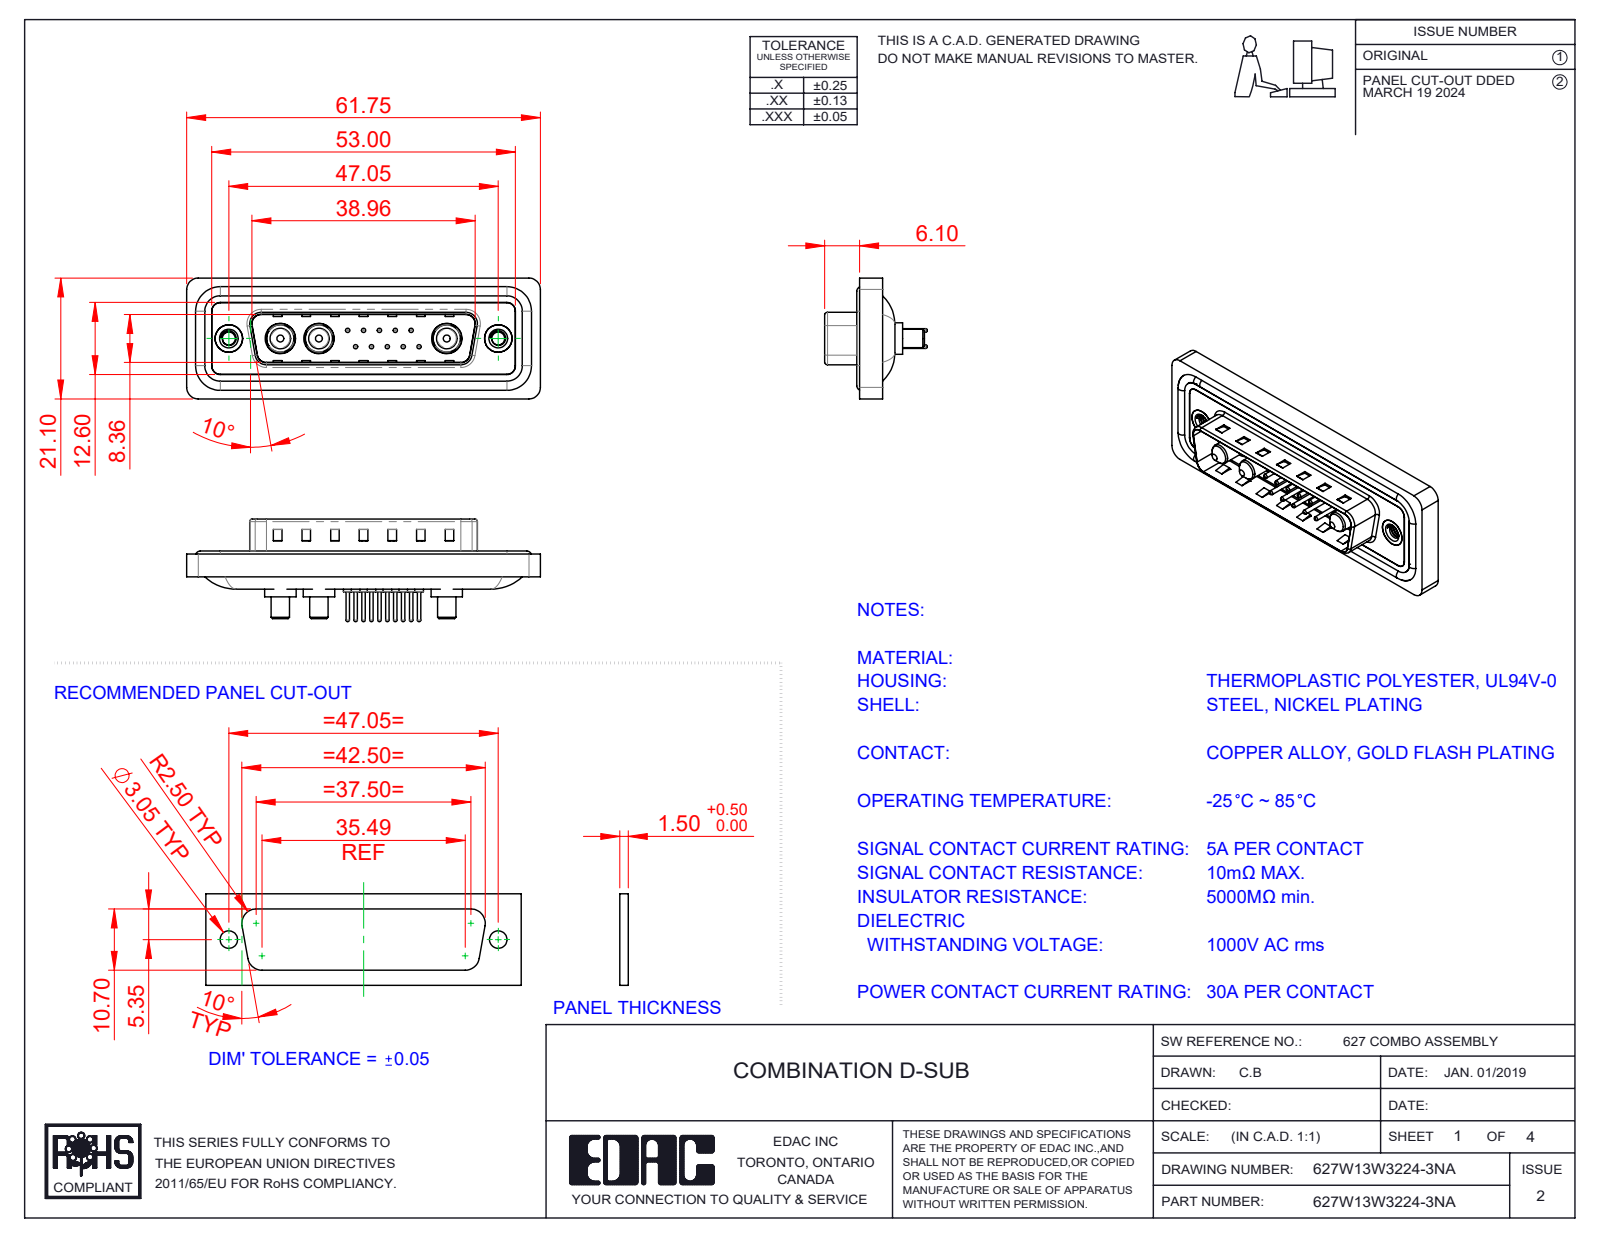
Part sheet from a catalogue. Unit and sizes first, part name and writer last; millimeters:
Units: millimetres
Overall size (bounding box): 61.75 × 21.1 × 17.9
Round holes (diameter × count): ⌀0.75 ×10, ⌀1.6 ×10, ⌀2 ×10, ⌀4.85 ×3, ⌀5.3 ×3, ⌀2.26 ×2, ⌀4 ×2, ⌀4.8 ×2, ⌀5 ×2
Round bosses / shafts (diameter × count): ⌀1.5 ×10, ⌀0.6 ×10, ⌀1.6 ×4, ⌀5.5 ×3, ⌀5.2 ×3, ⌀4.75 ×3, ⌀3.75 ×3, ⌀3.6 ×3
Partial cylindrical surfaces — rounded edges, fillets, slot ends (radius × count): R1.5 ×22, R2 ×18, R0.5 ×8, R1.6 ×8, R0.25 ×4, R0.6 ×4, R0.65 ×4, R0.9 ×4
Main face-to-face distances: 0.4, 1.5, 1.1, 1.6, 0.5, 3.1, 2.9, 0.82, 9.58, 4.1
Hole centre spacings: 3.16, 2.77, 5.04, 5.54, 7.49, 5.03, 8.31, 10.11
Volume: 7 358 mm³ · Surface area: 11 886 mm²
Bodies: 23 solids, 968 faces (309 planar, 387 cylindrical, 272 other)
Part name (STEP PRODUCT): 627Combo Housing_13W3; 627Combo Threaded Rivet_A; 627W13W3224-3NA; 627Combo Shell Rear_25 Contacts (+5 more)
STEP written by: SolidWorks 2023 (CONFIG_CONTROL_DESIGN)
